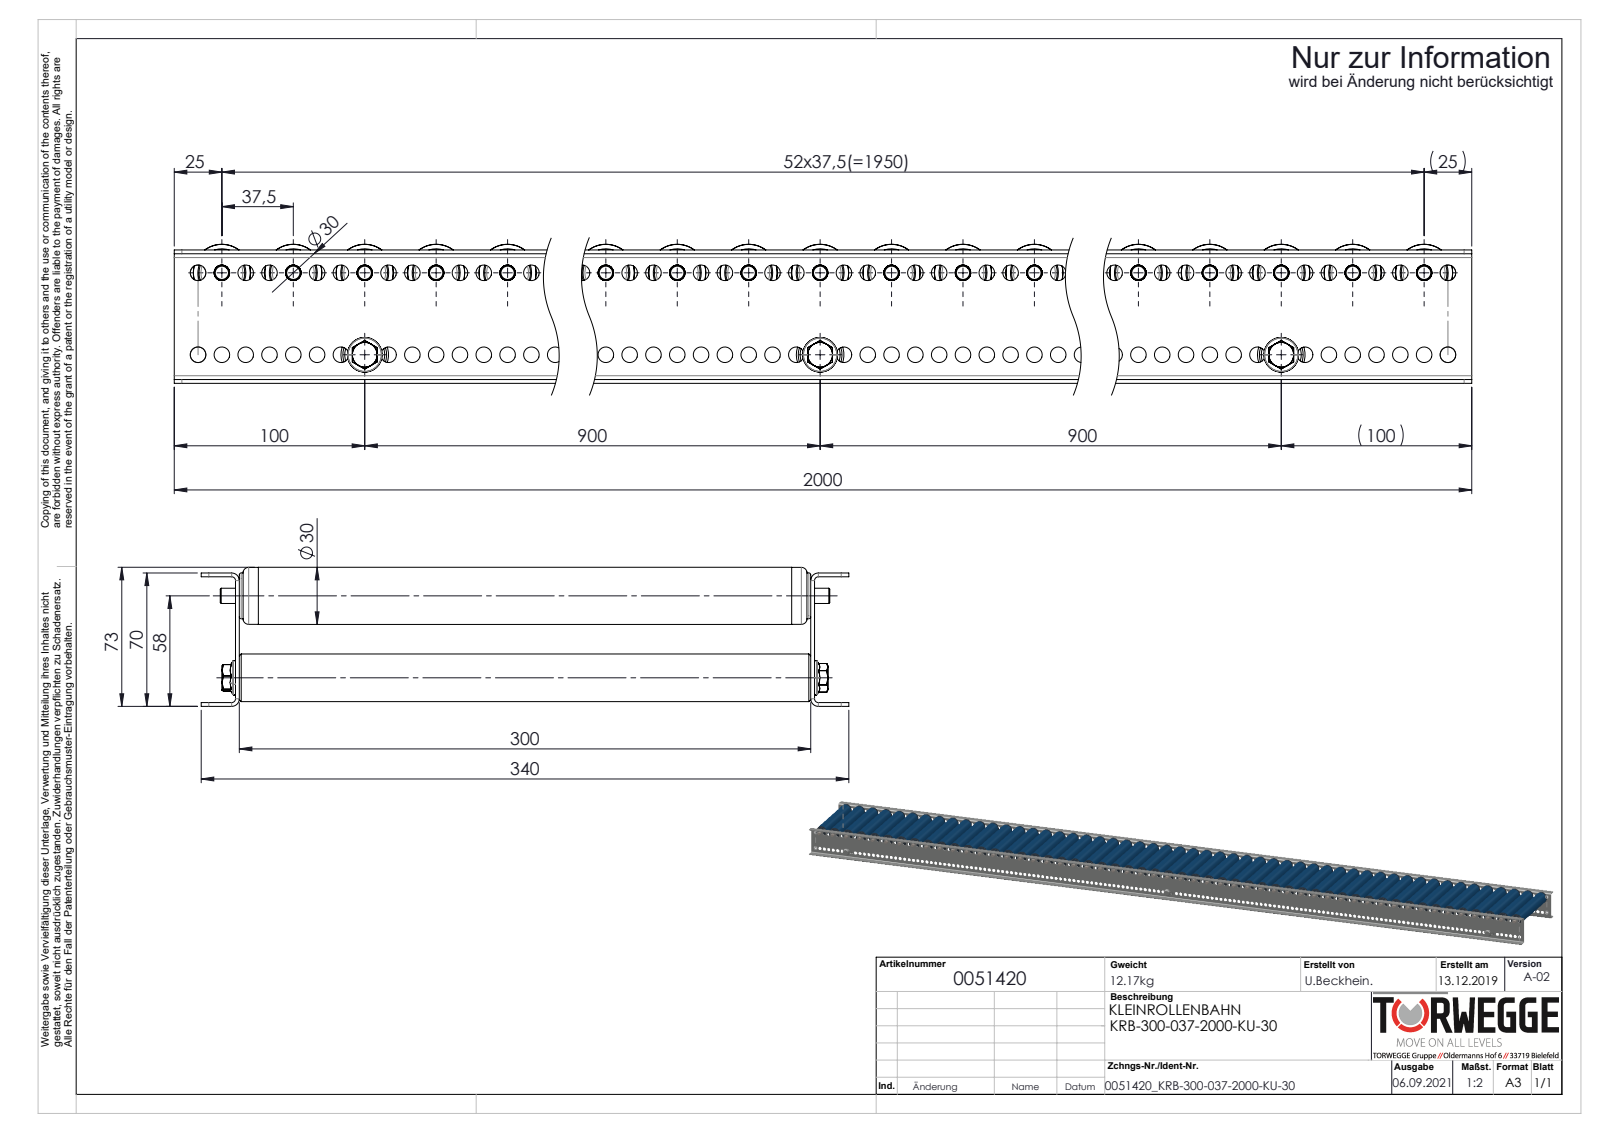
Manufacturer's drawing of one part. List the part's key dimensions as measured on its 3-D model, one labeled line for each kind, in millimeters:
Part name (STEP PRODUCT): S100995_TYP-KUT50-30x1,8-A8; S100994_Sperrzahnschraube_M08x16-8.8-A2K; 0051420; 0039778-Achse-ST-Ø08-KFG_AL320-G-FA (+4 more)
STEP written by: SolidWorks 2020 (AUTOMOTIVE_DESIGN)
Units: millimetres
Bodies: 123 solids, 12584 faces (3872 planar, 4740 cylindrical, 3972 other)
Overall size (bounding box): 2000 × 340 × 73
Volume: 4 150 000 mm³ · Surface area: 4 654 000 mm²
Round holes (diameter × count): ⌀8.2 ×318, ⌀8.1 ×53, ⌀22.6 ×53, ⌀25.2 ×53, ⌀6.8 ×3, ⌀21 ×3
Round bosses / shafts (diameter × count): ⌀8 ×56, ⌀30 ×53, ⌀29.9 ×53, ⌀26.5 ×53, ⌀26.4 ×53, ⌀24 ×53, ⌀25 ×3
Partial cylindrical surfaces — rounded edges, fillets, slot ends (radius × count): R5.05 ×53, R4 ×8, R2 ×4
Main face-to-face distances: 2, 302, 300, 68, 304, 70, 66, 10, 290, 12
Hole centre spacings: 12.5, 25, 37.5, 50, 62.5, 75, 87.5, 100
